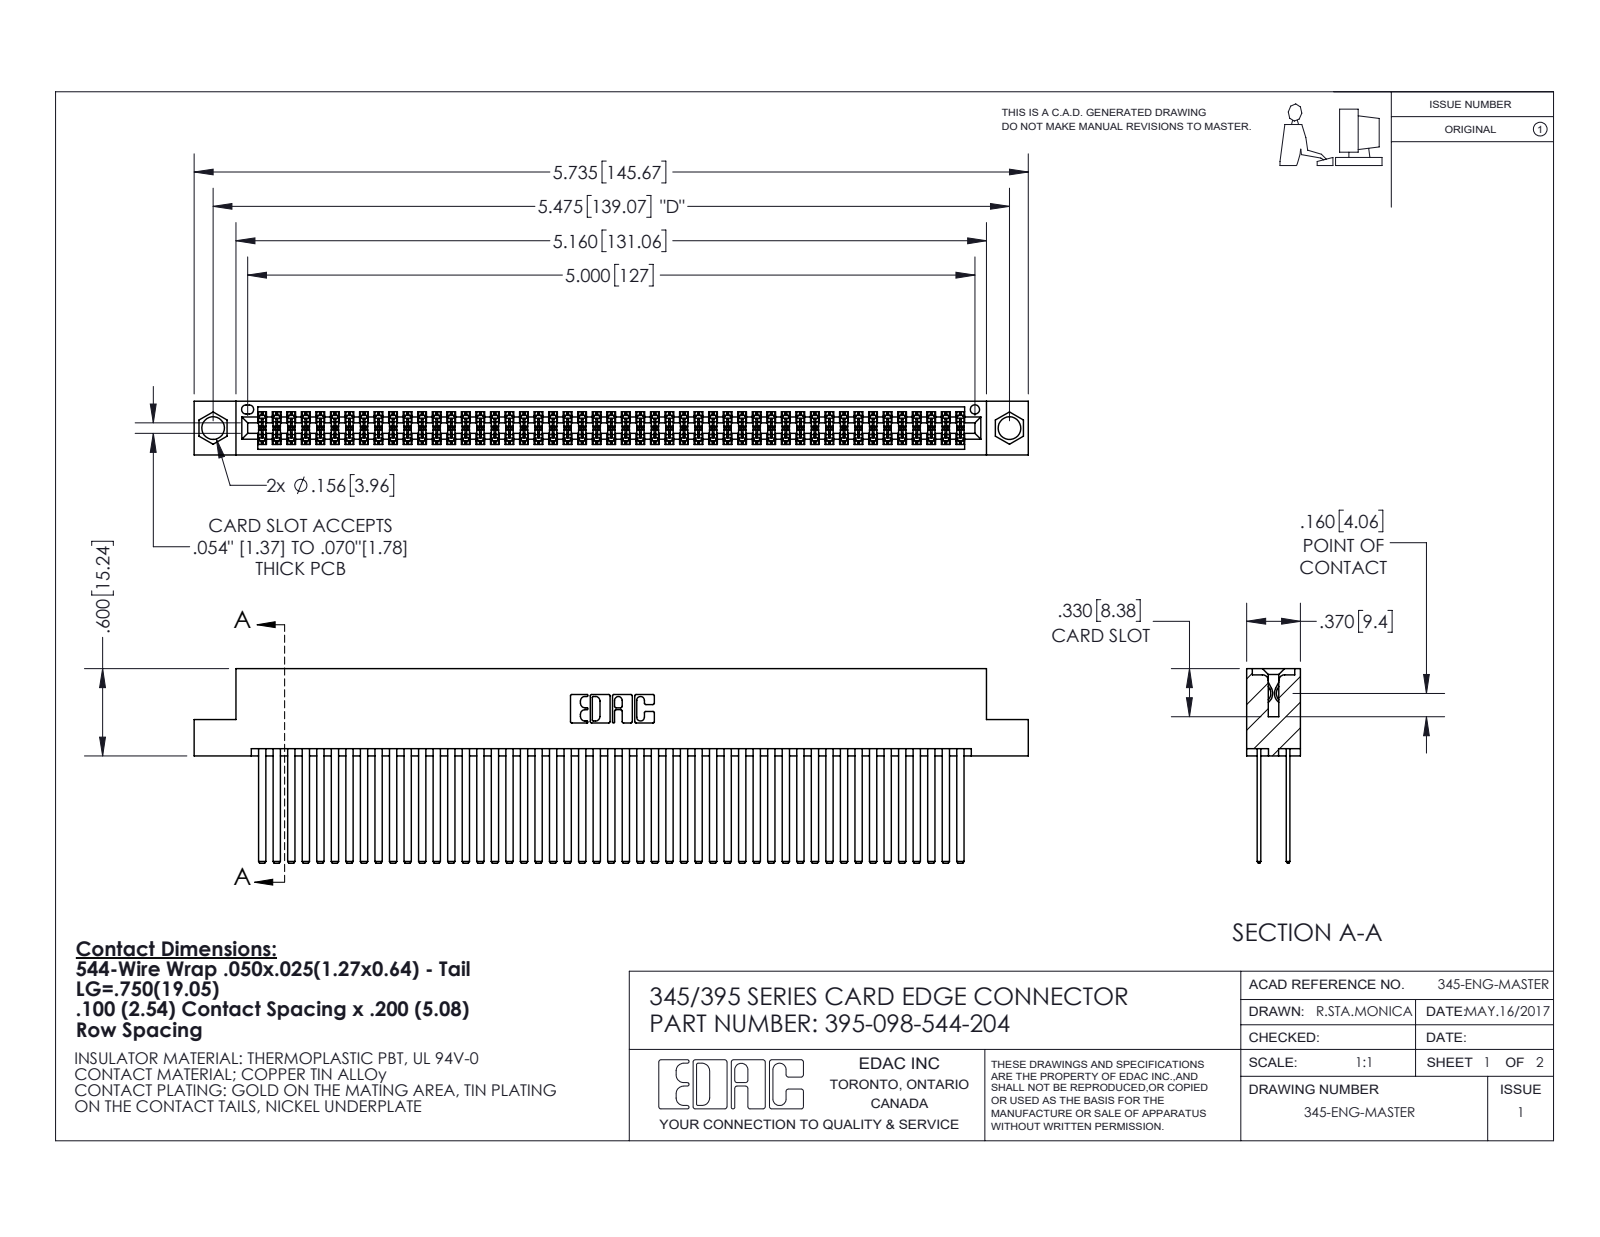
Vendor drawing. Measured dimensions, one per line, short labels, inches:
name: 345 Part_Flush Mounting Lugs - 0.156 Dia-TI; 395-098-544-204; 345-292-001_345-293-144
written by: SolidWorks 2020 (CONFIG_CONTROL_DESIGN)
unit: in
bodies: 99 solids, 4452 faces (2936 planar, 1516 cylindrical, 0 other)
size: 5.735 × 1.337 × 0.37
volume: 0.945 in³; area: 41.7 in²
holes: 2× ⌀0.156, 1× ⌀0.064
rounds: 147× R0.006, 22× R0.01, 6× R0.007, 6× R0.031, 3× R0.026, 2× R0.014, 2× R0.019, 2× R0.022
face distances: 0.2, 0.025, 0.298, 0.072, 0.098, 0.272, 0.225, 0.175, 0.37, 0.05
hole spacings: 0.27, 5.239, 5.475
